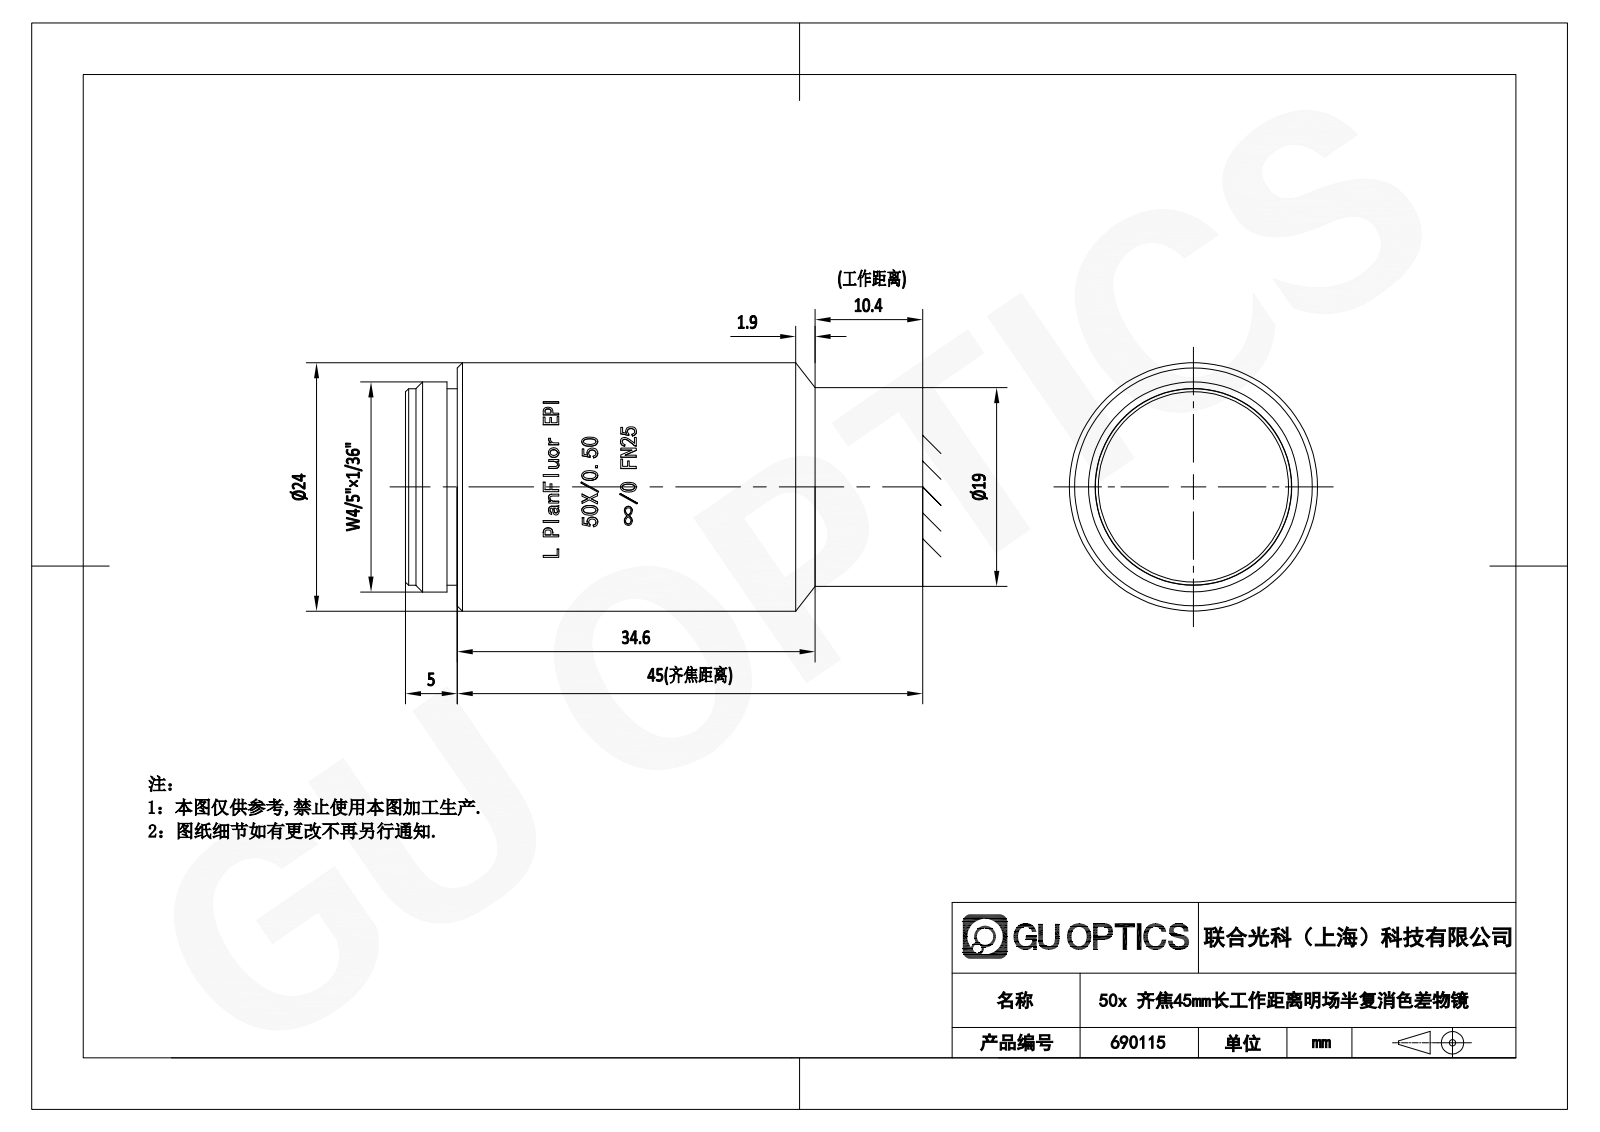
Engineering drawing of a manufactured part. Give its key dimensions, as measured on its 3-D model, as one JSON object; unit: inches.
{"part_name": "690115", "step_written_by": "SolidWorks 2020 (CONFIG_CONTROL_DESIGN)", "units": "inches", "bodies": {"solids": 1, "faces": 305, "planar": 132, "cylindrical": 46, "other": 127}, "overall_size": [1.559, 0.947, 0.945], "volume_in3": 1.038, "surface_area_in2": 5.825, "round_bosses_or_shafts": [[0.945, 1], [0.8, 1], [0.748, 1]], "partial_cylinders_radius": [[0.474, 1]], "face_to_face_distances": [1.559, 0.197, 1.362, 0.039, 0.157, 1.402, 0.118, 1.52, 0.148, 0.059]}
